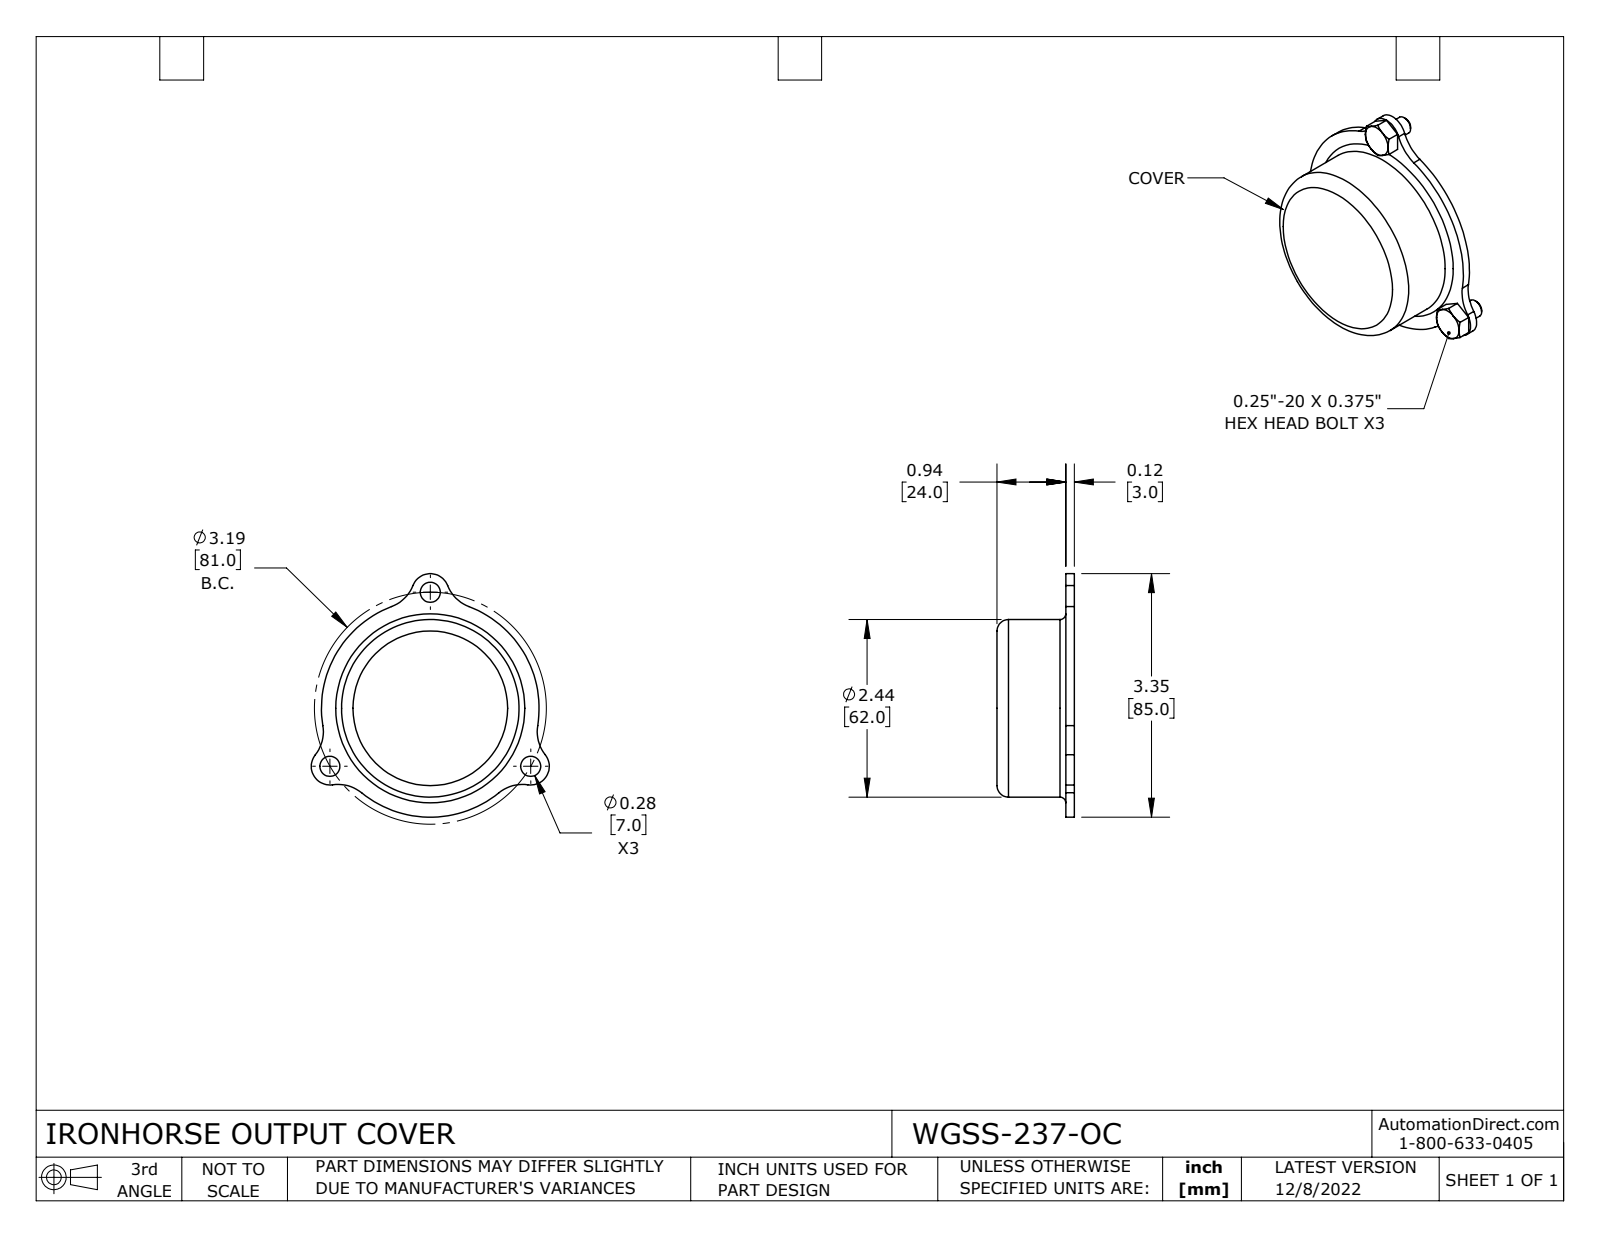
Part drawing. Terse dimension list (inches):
name: WGSS-237-OC
written by: SolidWorks 2021 (CONFIG_CONTROL_DESIGN)
unit: in
bodies: 4 solids, 94 faces (31 planar, 31 cylindrical, 32 other)
size: 3.346 × 3.274 × 1.32
volume: 1.354 in³; area: 31.84 in²
holes: 3× ⌀0.276, 1× ⌀2.283
bosses: 3× ⌀0.25, 1× ⌀2.441
rounds: 6× R0.512, 3× R0.256, 1× R1.496
face distances: 0.079, 0.866, 0.945, 0.118, 0.984, 1.063, 0.306, 0.188, 0.678, 0.757
hole spacings: 1.594, 2.762, 2.761
